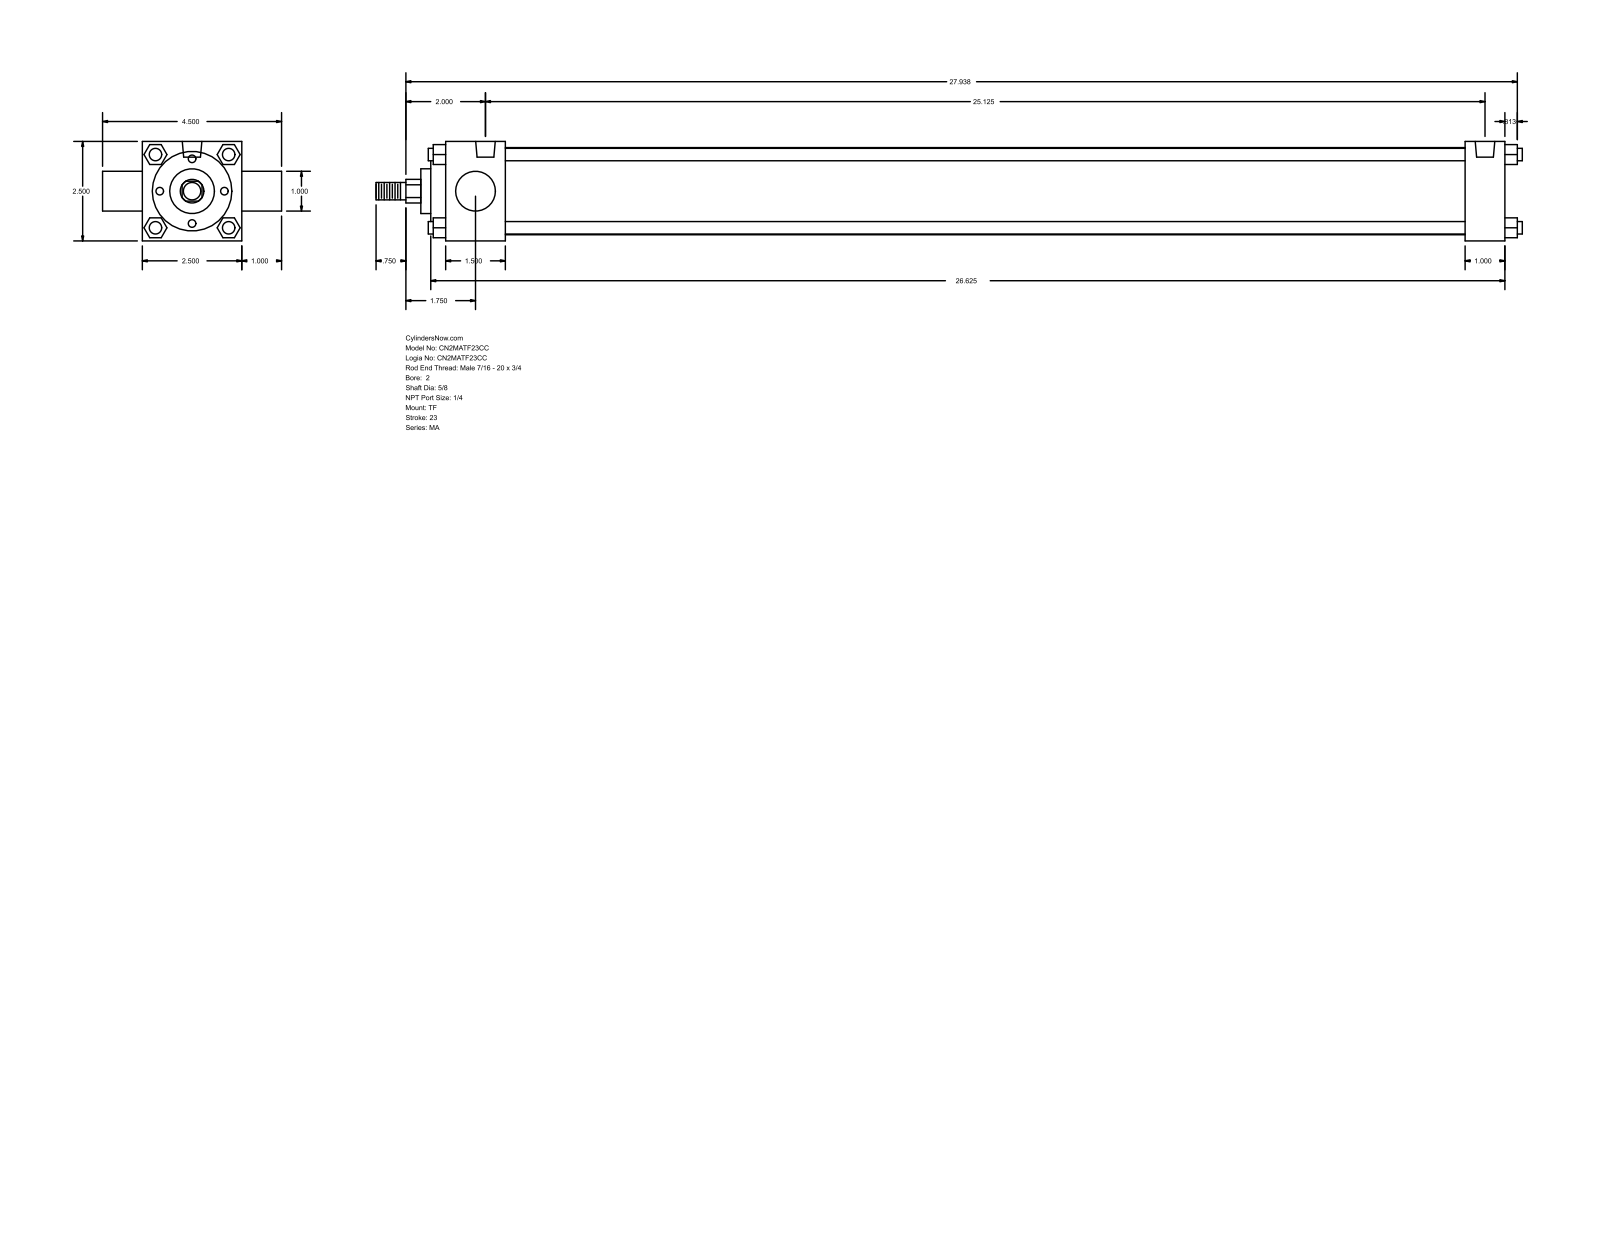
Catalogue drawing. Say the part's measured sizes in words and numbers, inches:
The part is named "MA_TF__0200_0.625". Its 3-D file was written by "GSSL Pune (CONFIG_CONTROL_DESIGN)". It is 0 solids with 122 faces: 93 planar, 29 cylindrical and 0 other. Overall it measures 28.813 by 4.5 by 2.5 inches. Round holes: 3 of diameter 0.313, 2 of diameter 0.492. Round bosses or shafts: 4 of diameter 0.313, 1 of diameter 2.19, 1 of diameter 2, 1 of diameter 1.125, 1 of diameter 1, 1 of diameter 0.625, 1 of diameter 0.437. Partial cylindrical surfaces (rounded edges, fillets, slot ends): 1 of radius 0.297. The main face-to-face distances are 2.5, 1, 1.5, 26.625, 0.5, 25.625, 24.125, 25.125, 0.375, 1.875. The hole center spacings are 25.125.
